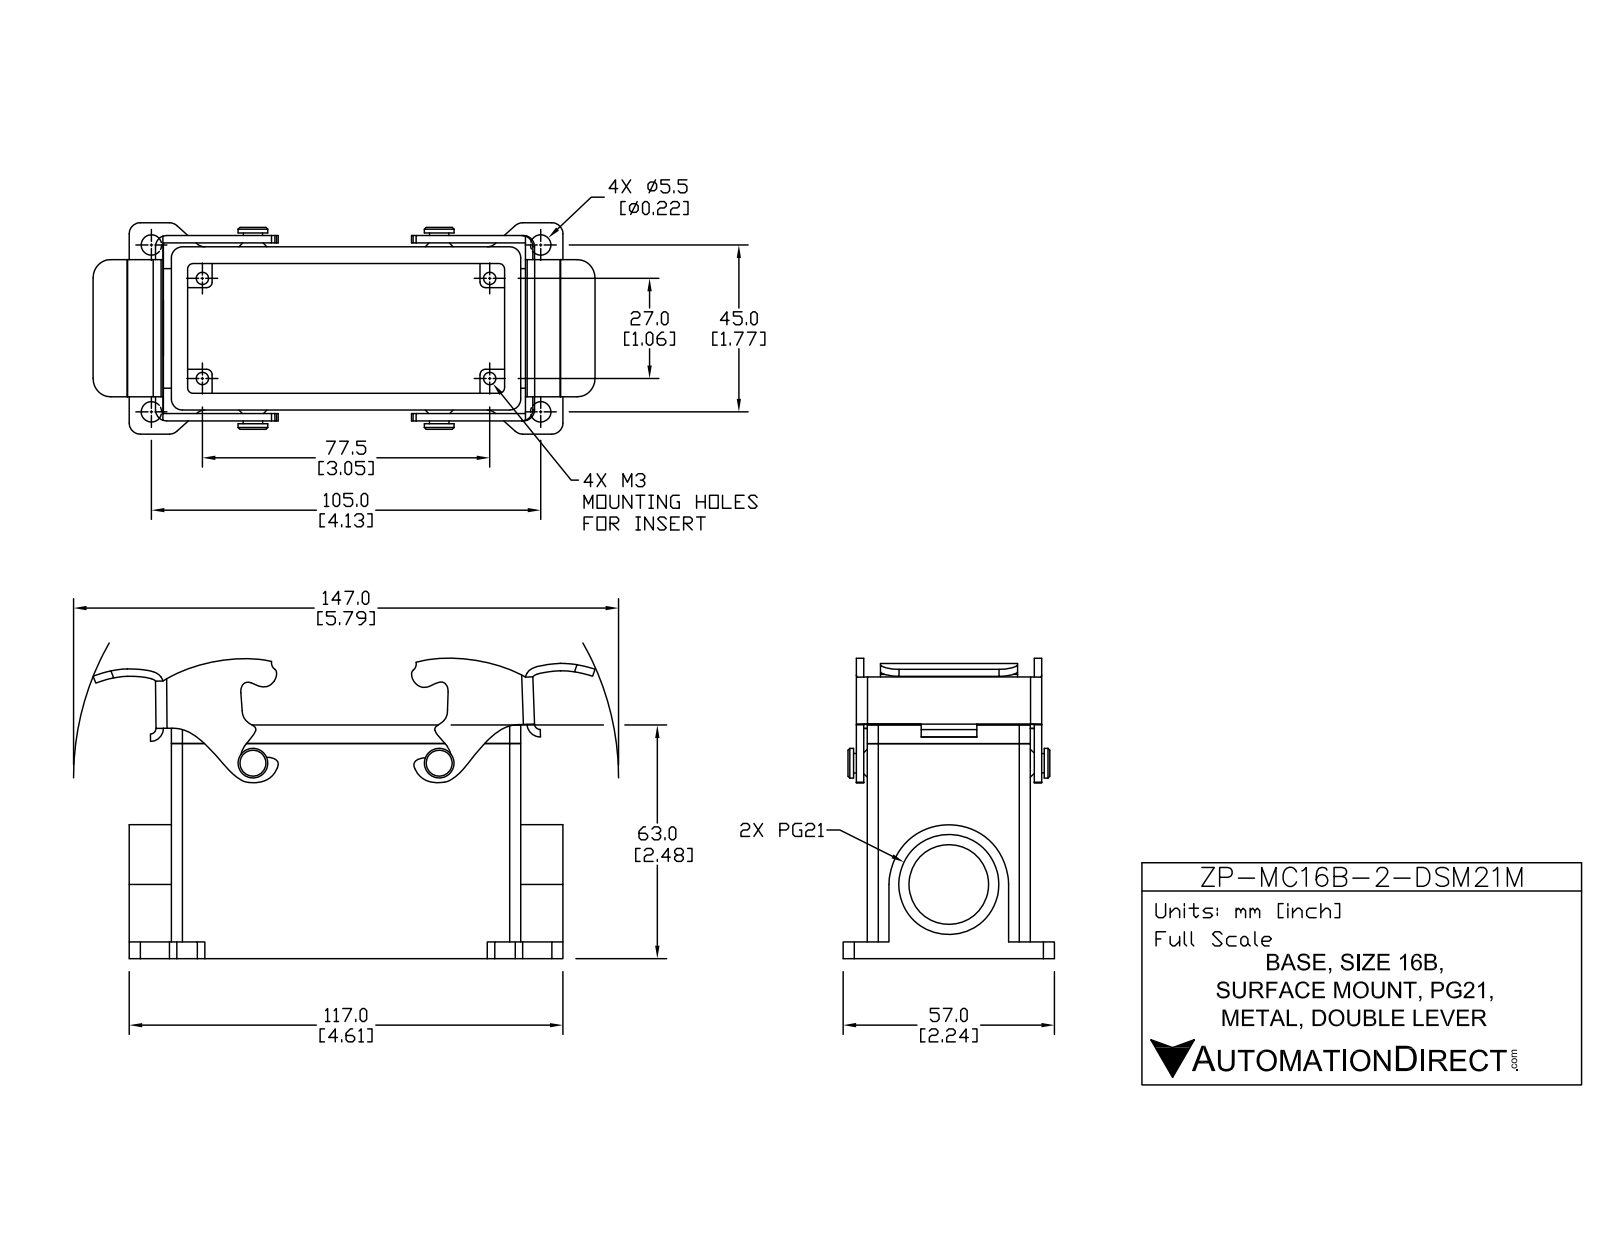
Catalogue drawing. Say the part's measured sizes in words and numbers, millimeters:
The part is named "ZP-MC16B-2-DSM21M". Its 3-D file was written by "SolidWorks 2011 (AUTOMOTIVE_DESIGN)". It is 4 solids with 307 faces: 125 planar, 174 cylindrical and 8 other. Overall it measures 146.34 by 77.17 by 57 millimeters. Its volume is 101 189 cubic millimeters and its surface area 59 406 square millimeters. Round holes: 4 of diameter 3.3, 4 of diameter 5.5, 1 of diameter 21.5, 1 of diameter 27. Round bosses or shafts: 2 of diameter 8, 2 of diameter 5.26, 2 of diameter 5.17. Partial cylindrical surfaces (rounded edges, fillets, slot ends): 26 of radius 0.5, 18 of radius 3, 8 of radius 1.5, 6 of radius 2, 6 of radius 4, 4 of radius 1, 4 of radius 10, 2 of radius 0.92. The main face-to-face distances are 4.5, 39.5, 44, 35, 1.15, 2, 57, 47.6, 55, 4.37. The hole center spacings are 16.43, 38.54, 91.69, 98.09, 27, 45, 77.5, 82.07.
